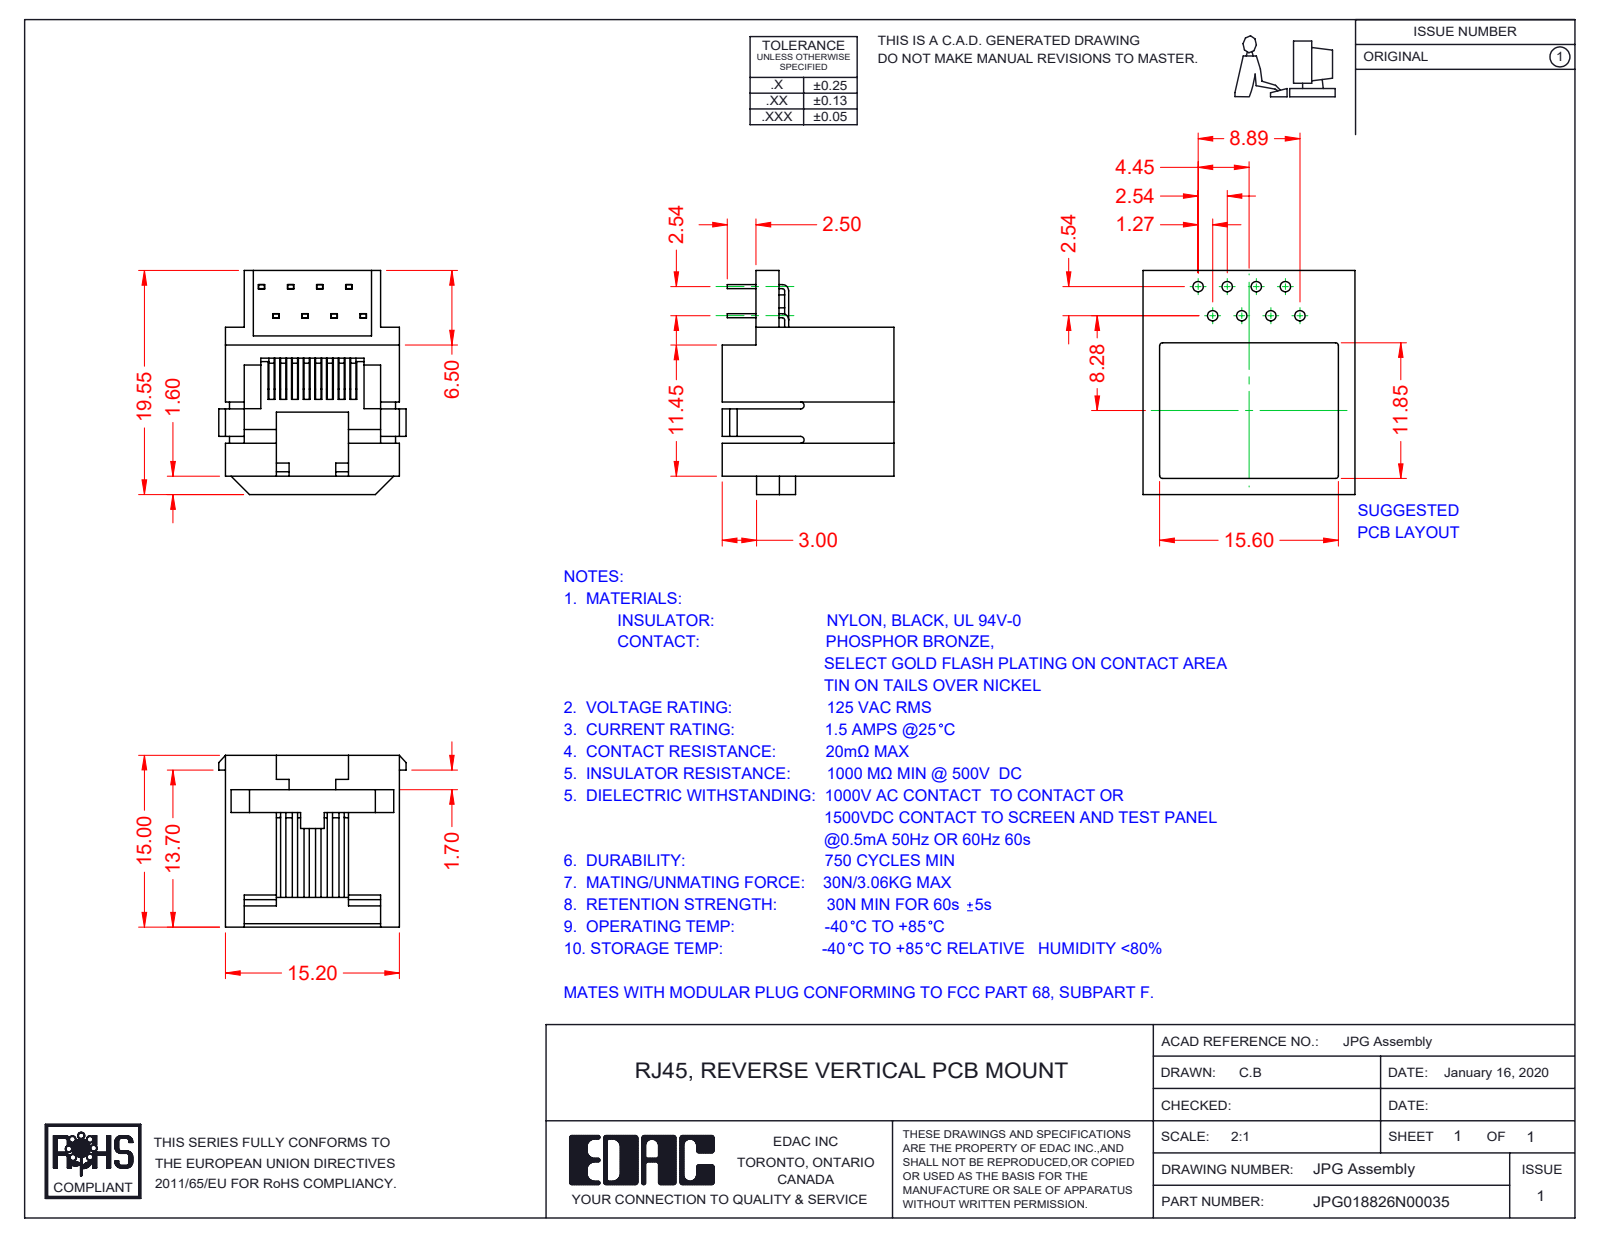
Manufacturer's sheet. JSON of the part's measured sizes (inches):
{"part_name": "PG Contact Lock; PG Contacts; JPG018826N00035; PG Insulator", "step_written_by": "SolidWorks 2016 (CONFIG_CONTROL_DESIGN)", "units": "inches", "bodies": {"solids": 10, "faces": 542, "planar": 461, "cylindrical": 69, "other": 12}, "overall_size": [0.77, 0.644, 0.591], "volume_in3": 0.085, "surface_area_in2": 4.196, "partial_cylinders_radius": [[0.012, 3], [0.008, 2], [0.014, 2], [0.022, 2], [0.028, 2]], "face_to_face_distances": [0.014, 0.065, 0.534, 0.406, 0.598, 0.102, 0.071, 0.024, 0.053, 0.508]}
